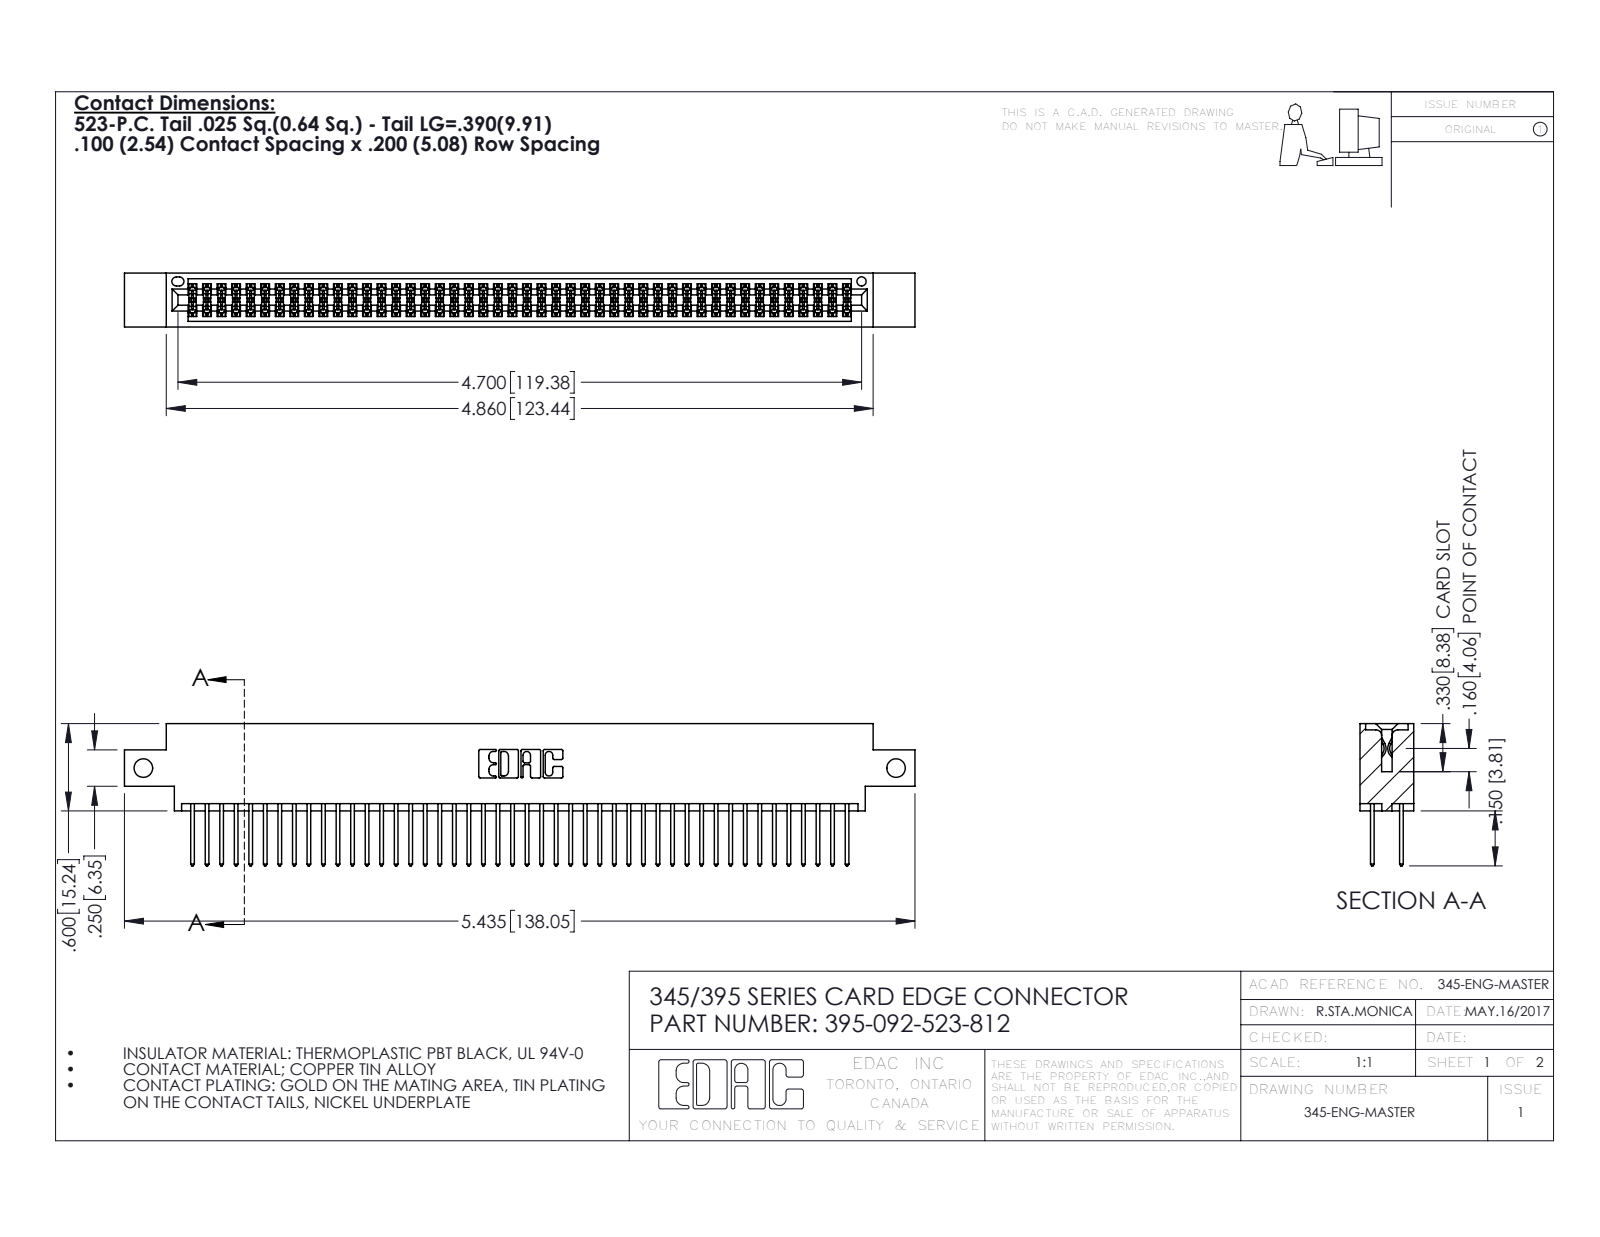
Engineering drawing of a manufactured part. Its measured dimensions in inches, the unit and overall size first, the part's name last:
Units: inches
Overall size (bounding box): 5.435 × 0.977 × 0.37
Round holes (diameter × count): ⌀0.128 ×2, ⌀0.064 ×1
Partial cylindrical surfaces — rounded edges, fillets, slot ends (radius × count): R0.006 ×138, R0.01 ×92, R0.01 ×22, R0.007 ×6, R0.031 ×6, R0.026 ×3, R0.014 ×2, R0.019 ×2
Main face-to-face distances: 0.298, 0.072, 0.2, 0.098, 0.272, 0.025, 0.37, 0.225, 0.175, 0.149
Hole centre spacings: 5.175
Volume: 0.82 in³ · Surface area: 32.23 in²
Bodies: 93 solids, 4730 faces (3120 planar, 1610 cylindrical, 0 other)
Part name (STEP PRODUCT): 345-292-001_345-293-123; 395-092-523-812; 345 Part_0.170 Offset - Side Mount
STEP written by: SolidWorks 2016 (CONFIG_CONTROL_DESIGN)
